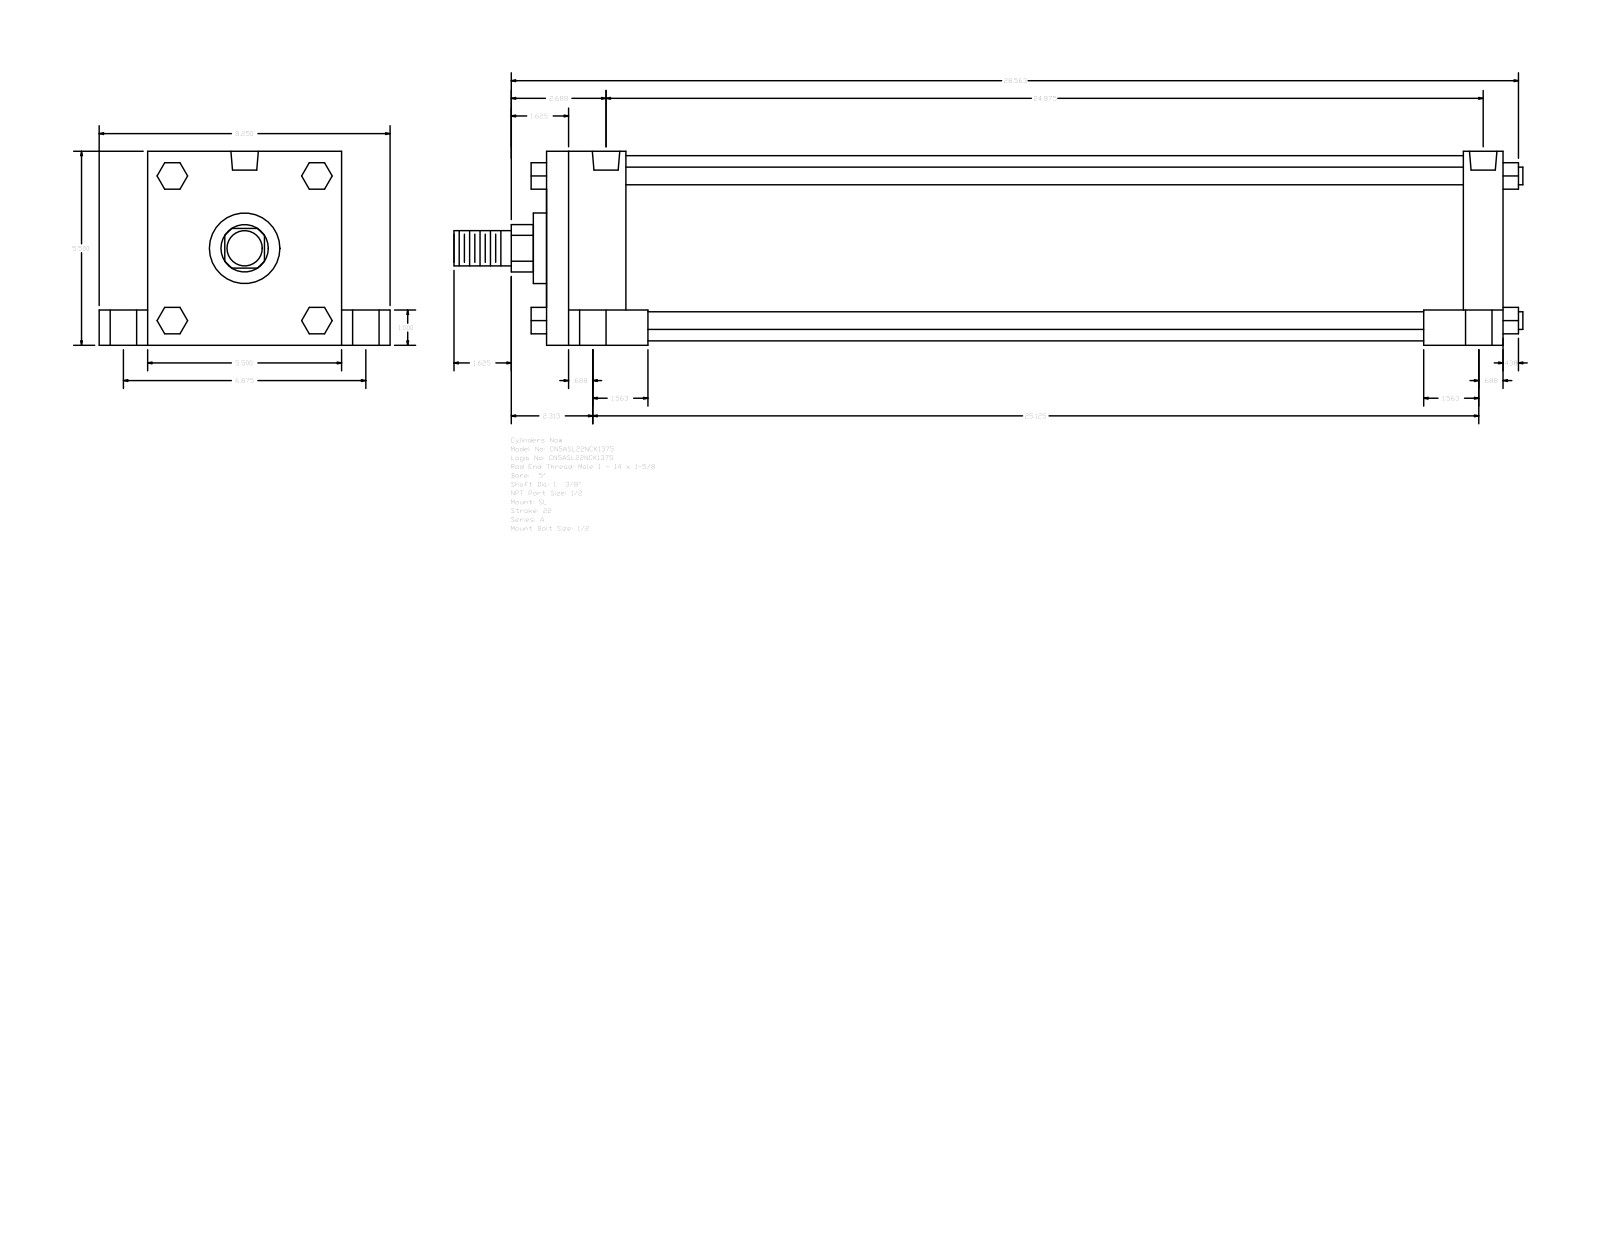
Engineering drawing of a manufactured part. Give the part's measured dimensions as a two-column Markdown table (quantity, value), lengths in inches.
| quantity | value |
| --- | --- |
| part name | A_SL__0500_1.375 |
| STEP written by | GSSL Pune (CONFIG_CONTROL_DESIGN) |
| units | inches |
| bodies | 0 solids, 150 faces (114 planar, 36 cylindrical, 0 other) |
| overall size | 30.313 × 8.25 × 5.5 |
| round holes (diameter × count) | 0.344 × 4, 0.75 × 4, 1 × 4, 0.778 × 2 |
| round bosses / shafts (diameter × count) | 0.5 × 4, 5.25 × 1, 2 × 1, 1.375 × 1, 1 × 1 |
| partial cylindrical surfaces (radius × count) | 0.672 × 1 |
| main face-to-face distances | 5.5, 27.125, 2.25, 24.875, 1, 4.5, 1.375, 6.875, 1.125, 26 |
| hole center spacings | 0.094, 3.437, 3.44, 3.458, 3.469, 6.875, 24.687, 24.781 |
